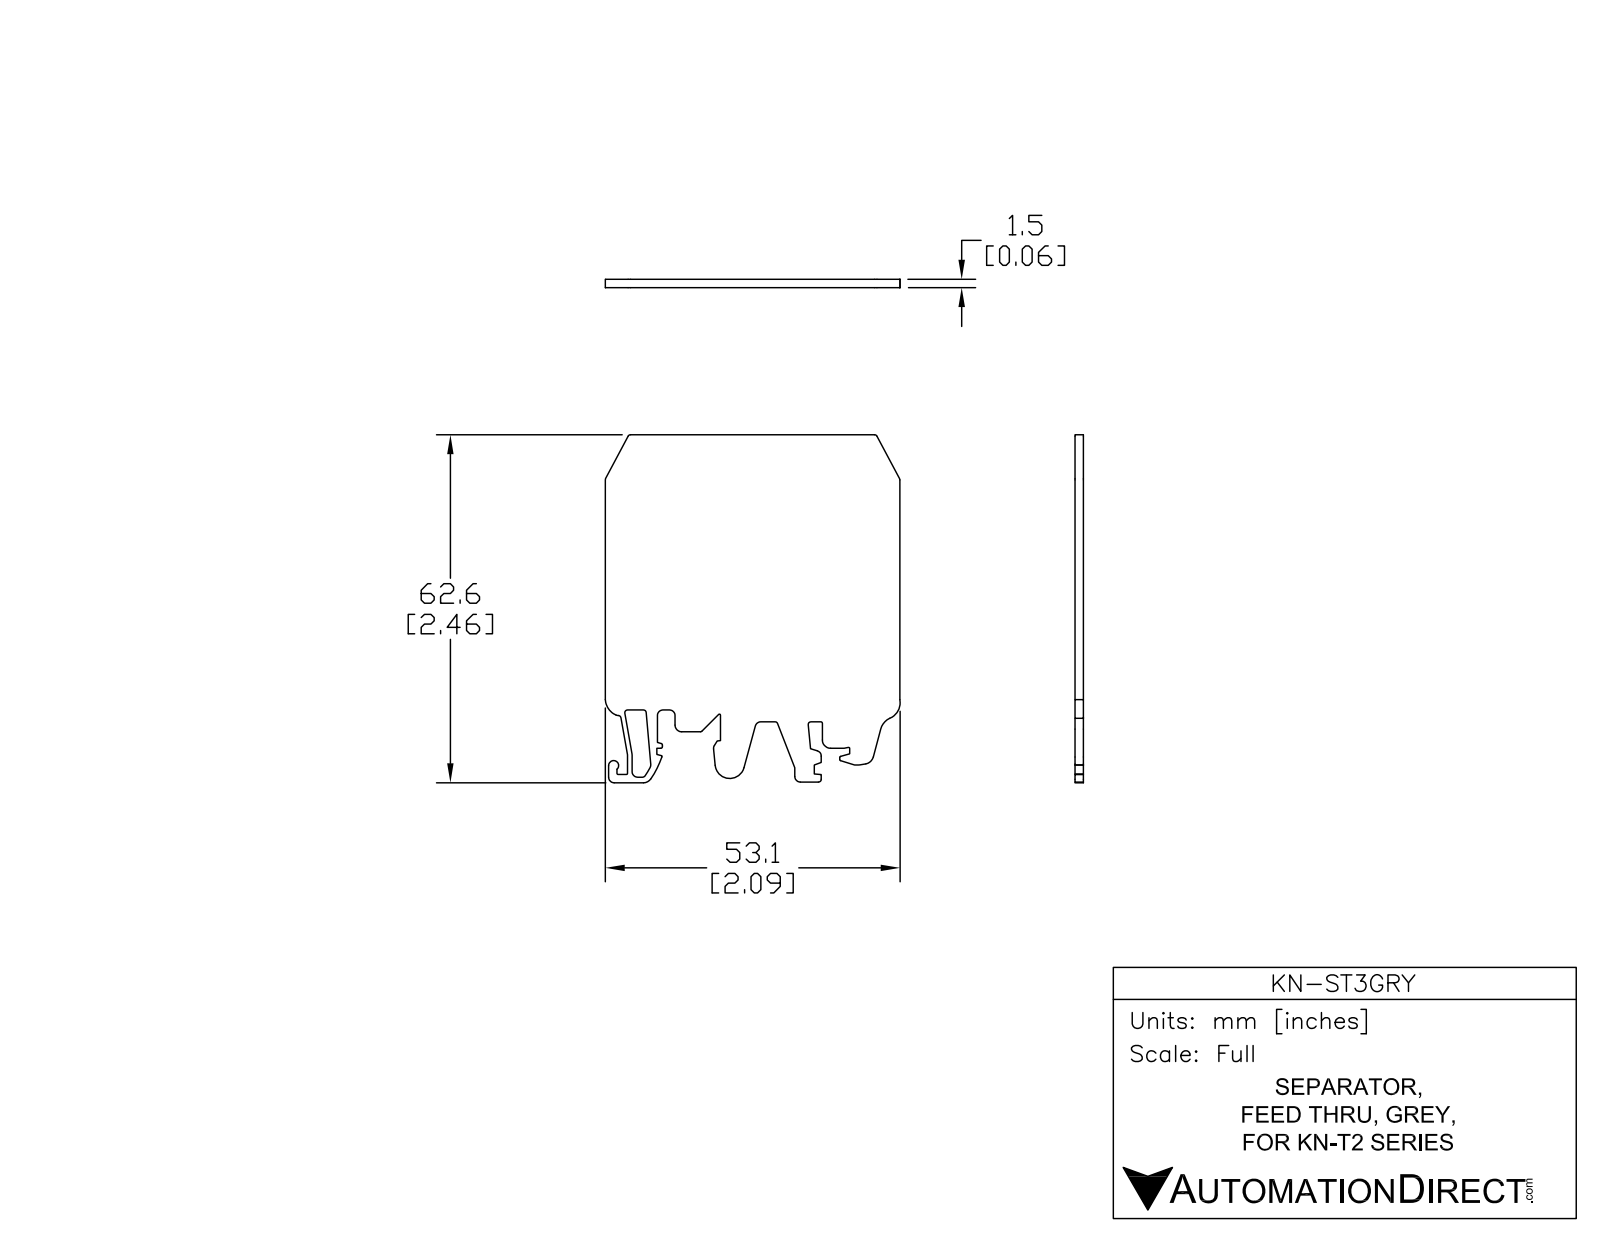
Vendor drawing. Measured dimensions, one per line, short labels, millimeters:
name: KN-ST3
written by: SolidWorks 2014 (AUTOMOTIVE_DESIGN)
unit: mm
bodies: 1 solid, 105 faces (56 planar, 49 cylindrical, 0 other)
size: 62.6 × 53.05 × 1.5
volume: 4 346 mm³; area: 6 283 mm²
rounds: 10× R0.5, 8× R1, 6× R0.2, 5× R0.3, 2× R1, 2× R1.5, 2× R3, 1× R0.5
face distances: 1.5, 53, 0.83, 62.6, 9.39, 43.61, 20.74, 11.35, 32.26, 10.98
